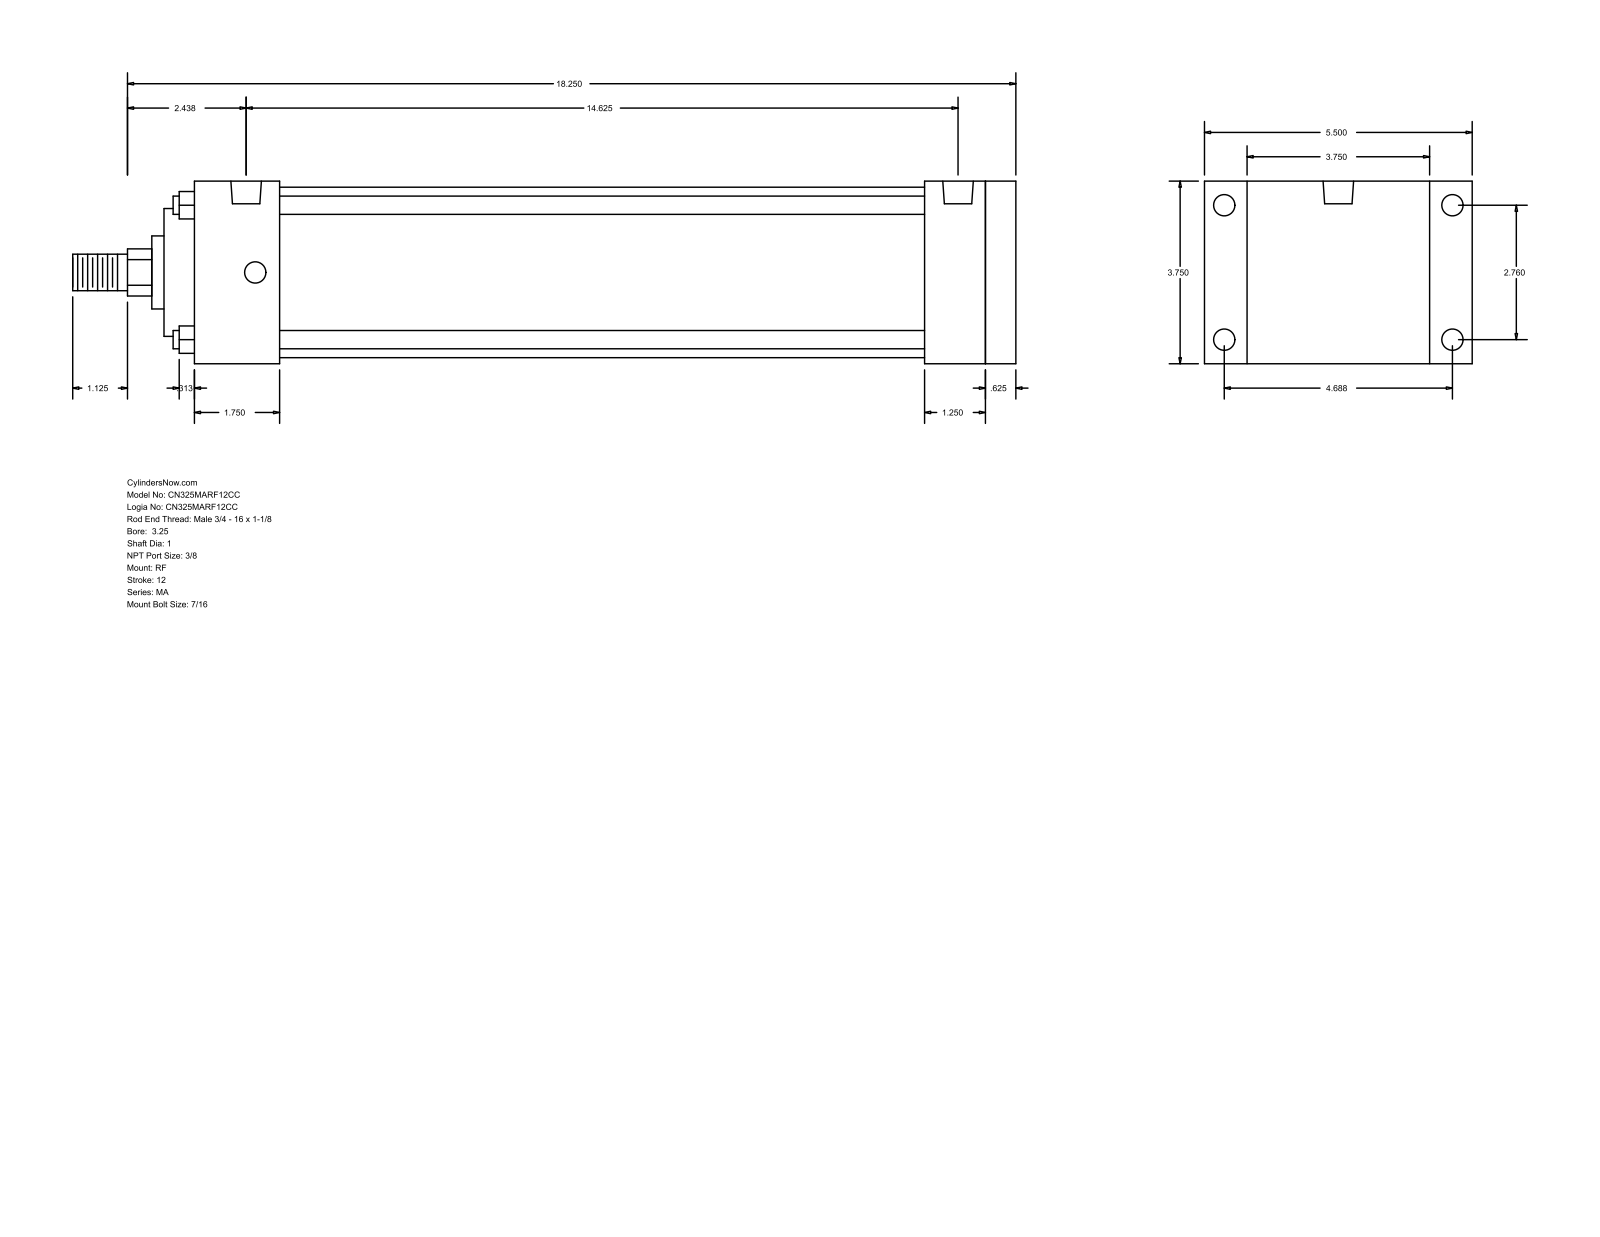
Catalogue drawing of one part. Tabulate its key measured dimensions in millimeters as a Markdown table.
| quantity | value |
| --- | --- |
| part name | MA_RF__0325_1 |
| STEP written by | GSSL Pune (CONFIG_CONTROL_DESIGN) |
| units | millimeters |
| bodies | 0 solids, 94 faces (65 planar, 29 cylindrical, 0 other) |
| overall size | 492.12 × 139.7 × 95.25 |
| round holes (diameter × count) | 11.11 × 8, 15.93 × 2 |
| round bosses / shafts (diameter × count) | 9.53 × 4, 88.9 × 1, 66.67 × 1, 38.1 × 1, 25.4 × 1, 19.05 × 1 |
| partial cylindrical surfaces (radius × count) | 12.29 × 1 |
| main face-to-face distances | 95.24, 428.63, 15.87, 412.76, 22.23, 117.47, 47.62, 444.5, 381.01, 31.75 |
| hole center spacings | 70.1, 119.06, 138.16, 361.95, 4.76, 4.77, 366.71, 366.72 |
